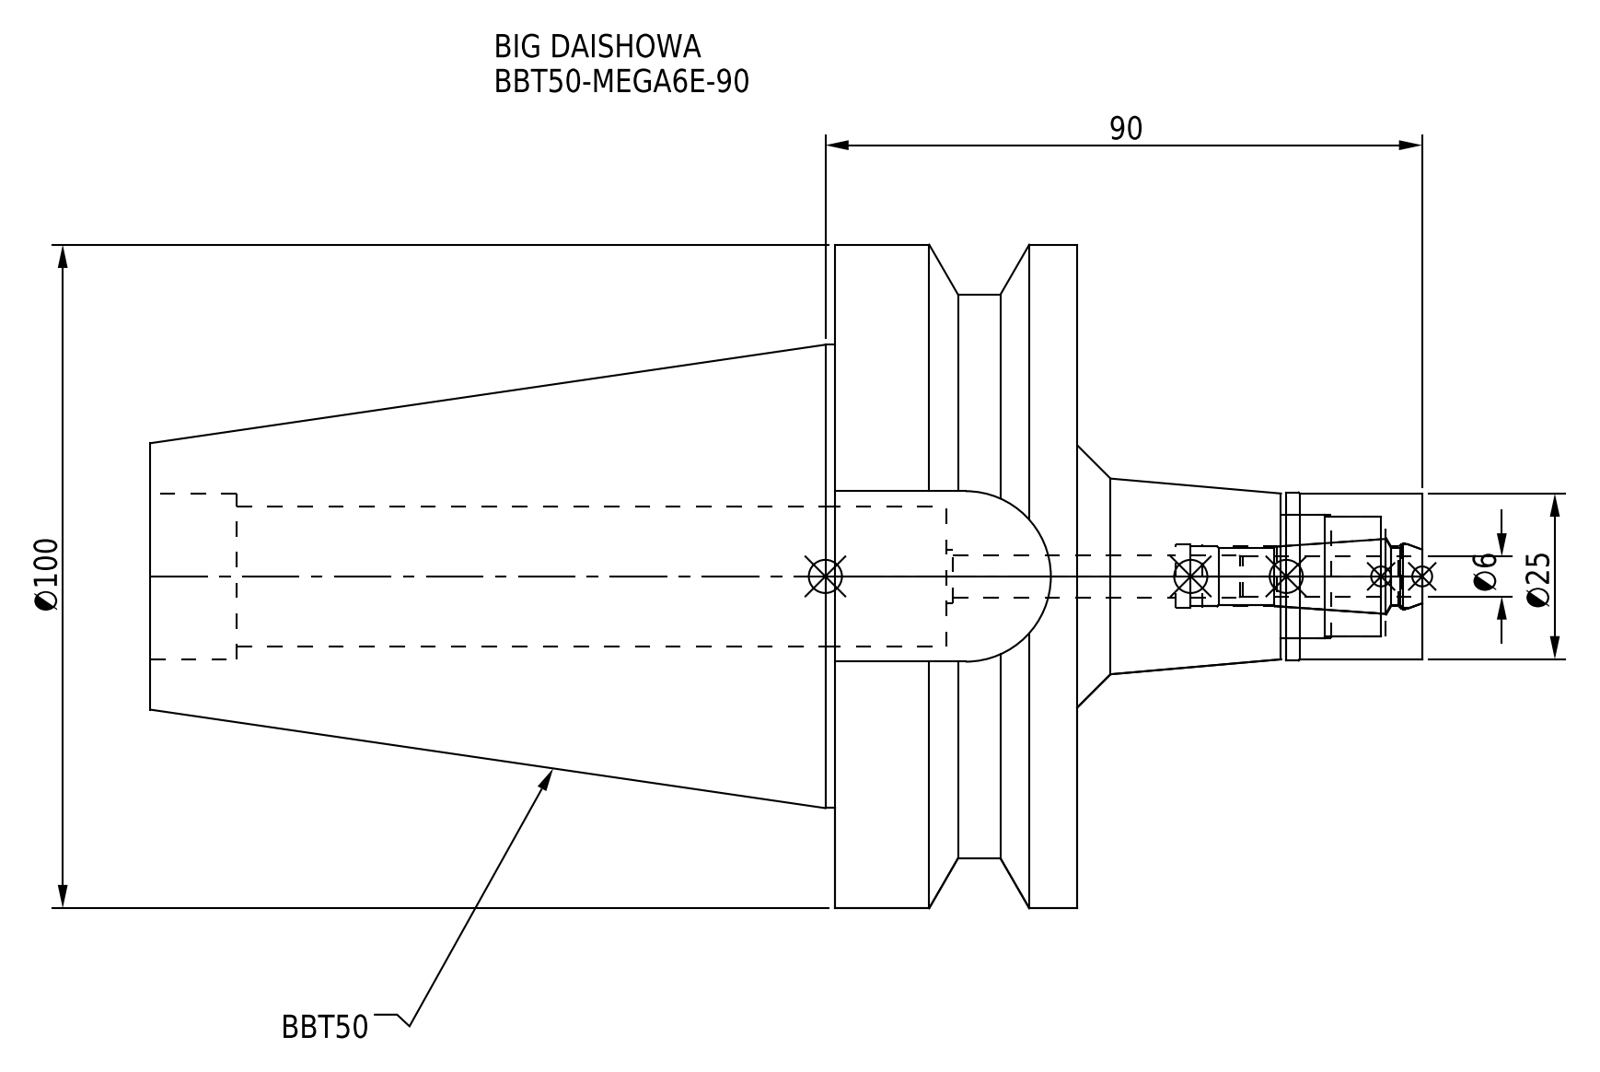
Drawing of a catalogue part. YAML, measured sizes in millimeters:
part_name: "BBT50ME06090-060_ASM.stp; MEN6_1.stp; DXF_TEMP_ASSY_ASM_4_ASM.stp; BBT50-MEGA6E-90 (+3 more)"
step_written_by: "SolidWorks 2019 (CONFIG_CONTROL_DESIGN)"
units: millimeters
bodies: {solids: 2, faces: 81, planar: 21, cylindrical: 40, other: 20}
overall_size: [191.8, 100, 100]
volume: 480884
surface_area: 61672
round_holes:
  - {diameter: 6.4, count: 1}
  - {diameter: 8, count: 1}
  - {diameter: 9, count: 1}
  - {diameter: 9.6, count: 1}
  - {diameter: 9.9, count: 1}
  - {diameter: 18, count: 1}
  - {diameter: 18.5, count: 1}
  - {diameter: 21.2, count: 1}
  - {diameter: 25, count: 1}
round_bosses_or_shafts:
  - {diameter: 100, count: 1}
  - {diameter: 85, count: 1}
  - {diameter: 69.85, count: 1}
  - {diameter: 25.3, count: 1}
partial_cylinders:
  - {radius: 12.85, count: 1}
face_to_face_distances: [36.5, 70.8, 139.8, 103.3, 25.7, 52, 88.5, 191.8, 16.7, 71.8]
